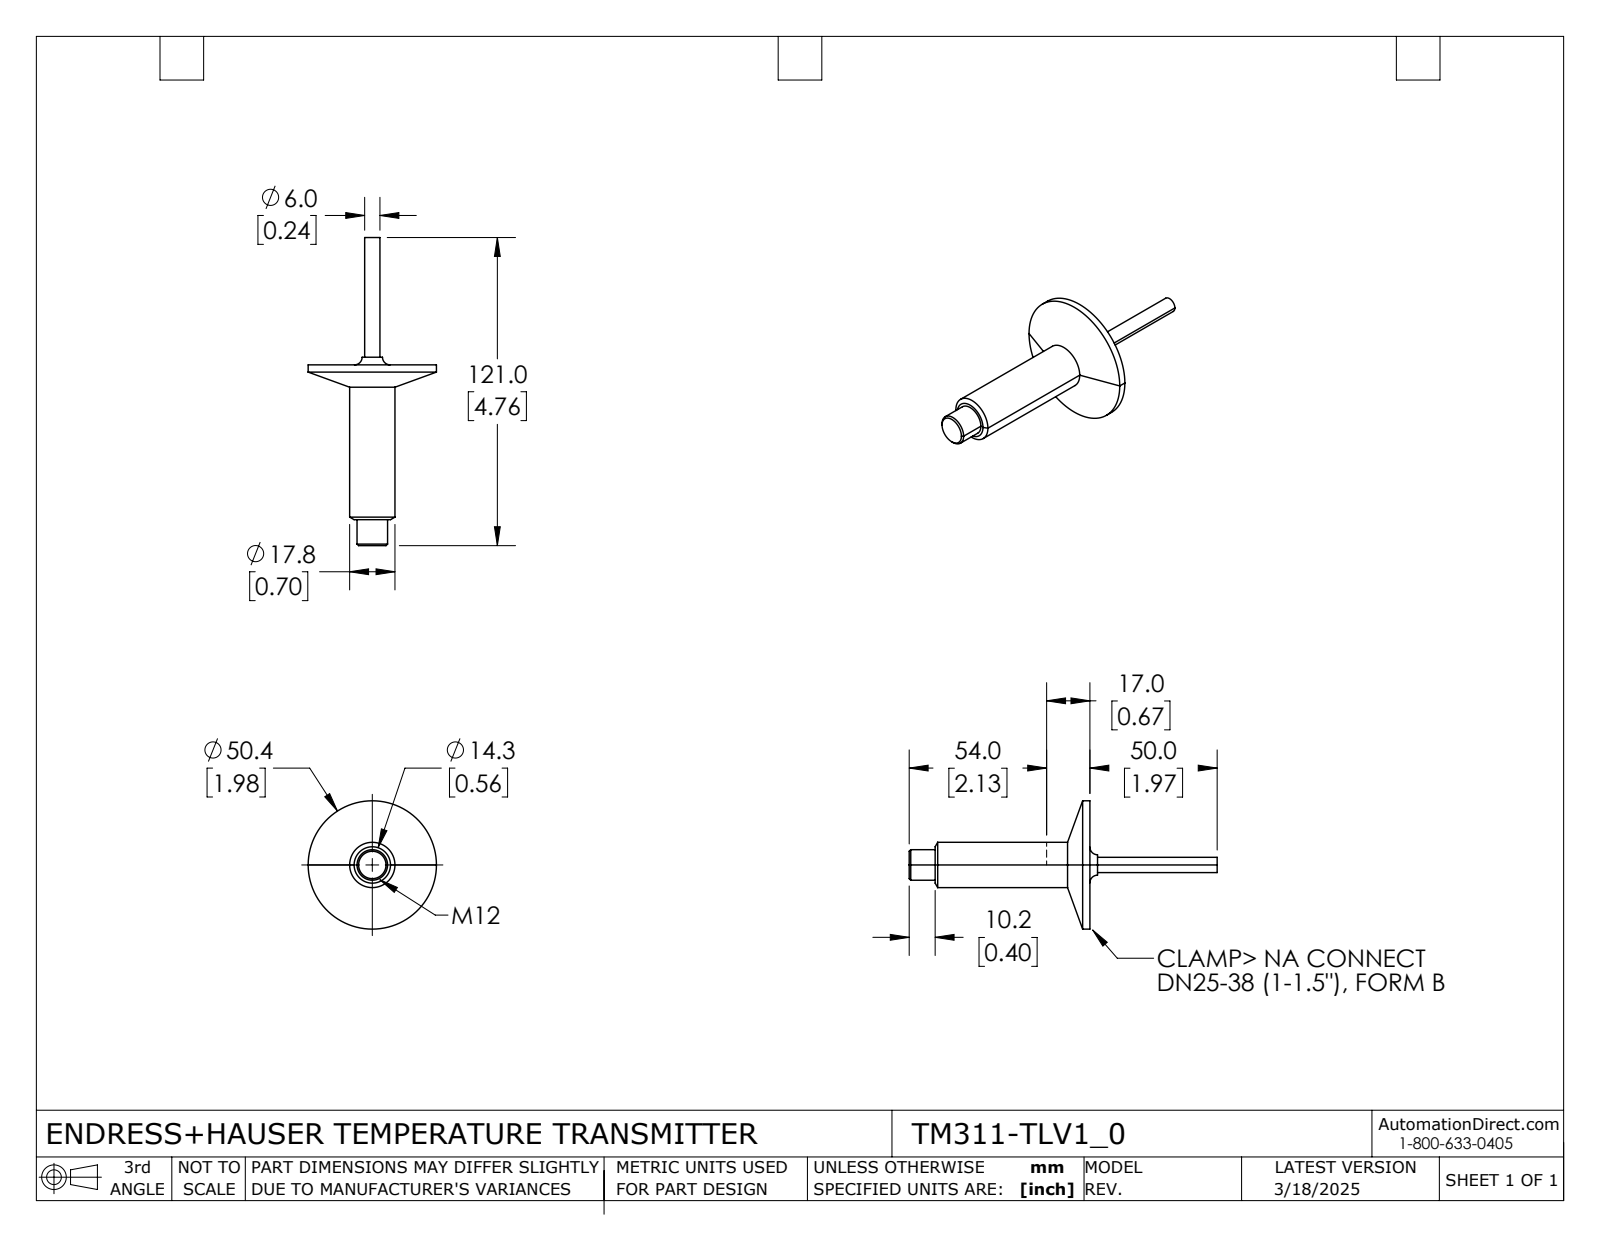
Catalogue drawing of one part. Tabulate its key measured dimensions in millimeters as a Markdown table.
| quantity | value |
| --- | --- |
| part name | TM311-TLV1_0 |
| STEP written by | SolidWorks 2021 (AUTOMOTIVE_DESIGN) |
| units | millimeters |
| bodies | 1 solid, 29 faces (6 planar, 8 cylindrical, 15 other) |
| overall size | 121 × 50.4 × 50.4 |
| volume | 26 630 mm³ |
| surface area | 8 961 mm² |
| round bosses / shafts (diameter × count) | 50.4 × 1, 17.8 × 1, 12 × 1, 6 × 1 |
| main face-to-face distances | 71, 60.8, 10.2, 50, 110.8, 121, 47, 3, 63.8, 74 |
